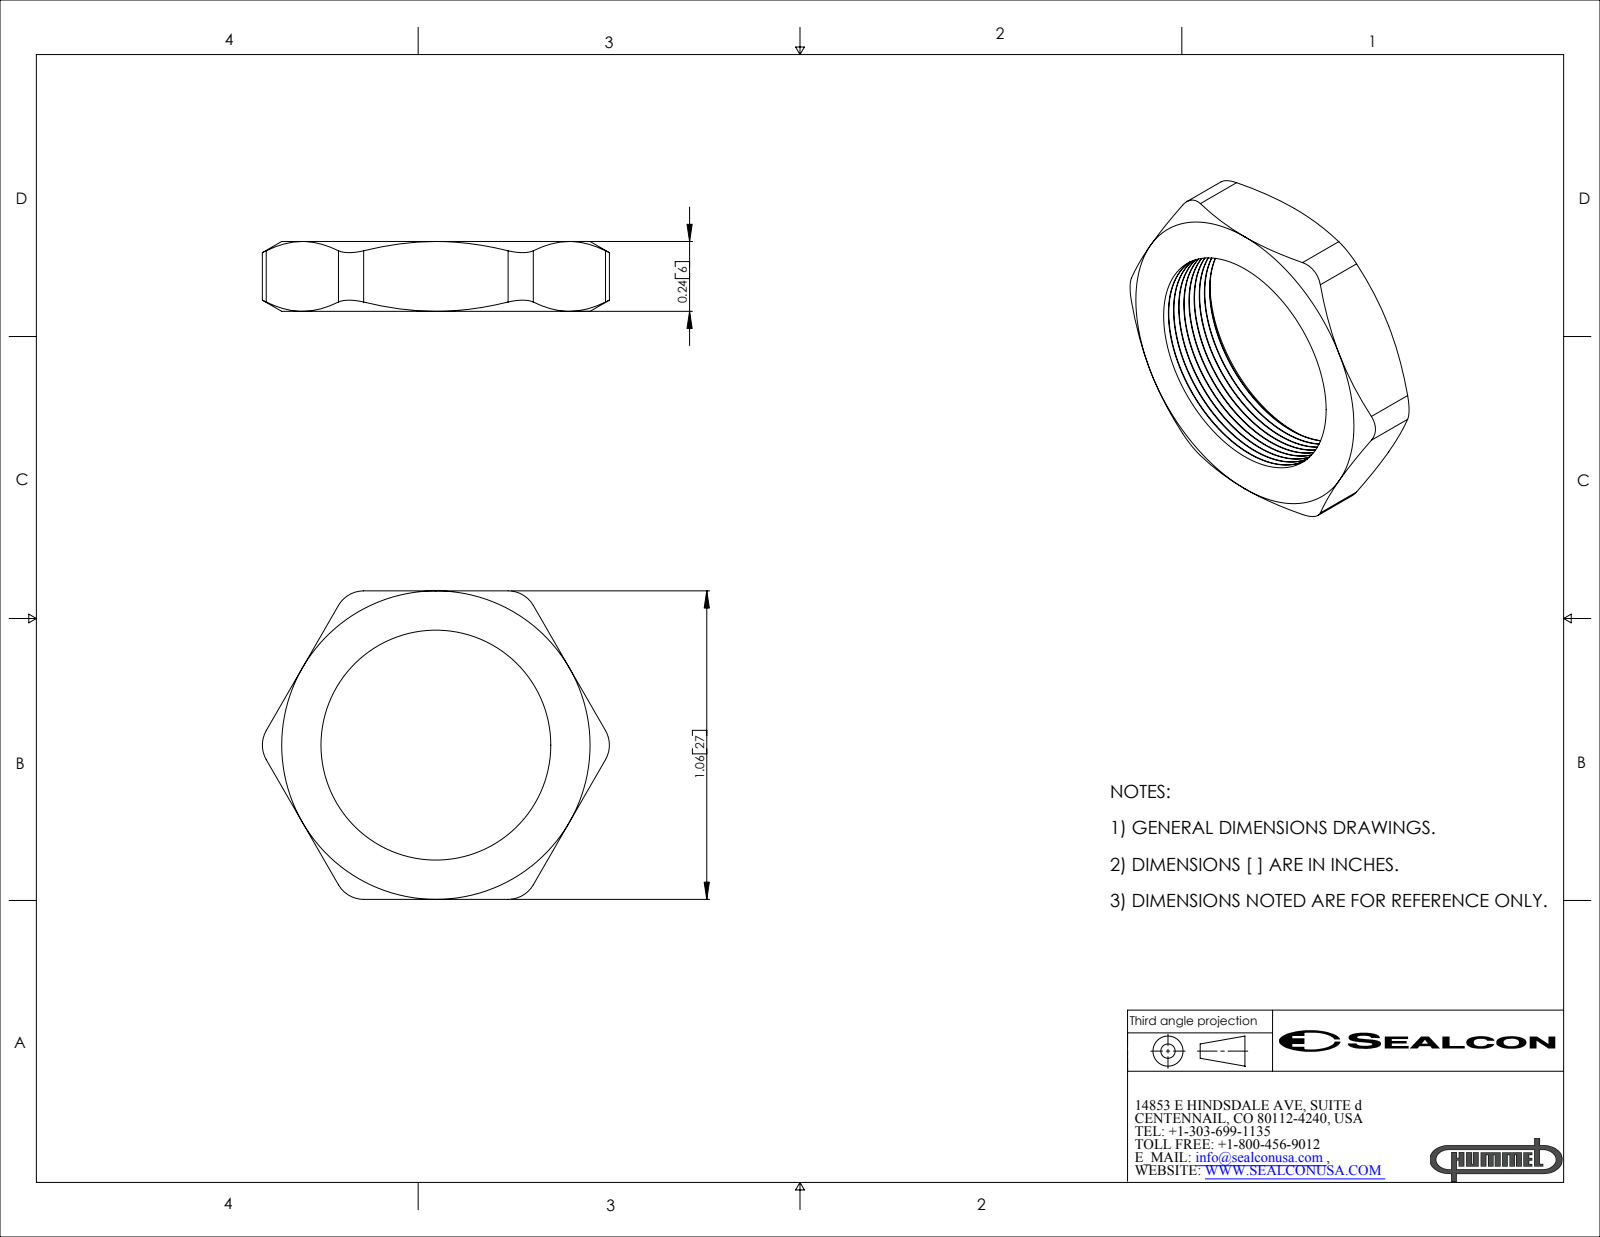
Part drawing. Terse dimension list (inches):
name: NM-20-GY
written by: SolidWorks 2007 (CONFIG_CONTROL_DESIGN)
unit: in
bodies: 1 solid, 87 faces (8 planar, 25 cylindrical, 54 other)
size: 1.193 × 1.06 × 0.24
volume: 0.107 in³; area: 2.884 in²
holes: 1× ⌀0.79
rounds: 6× R0.1
face distances: 0.24, 1.06
